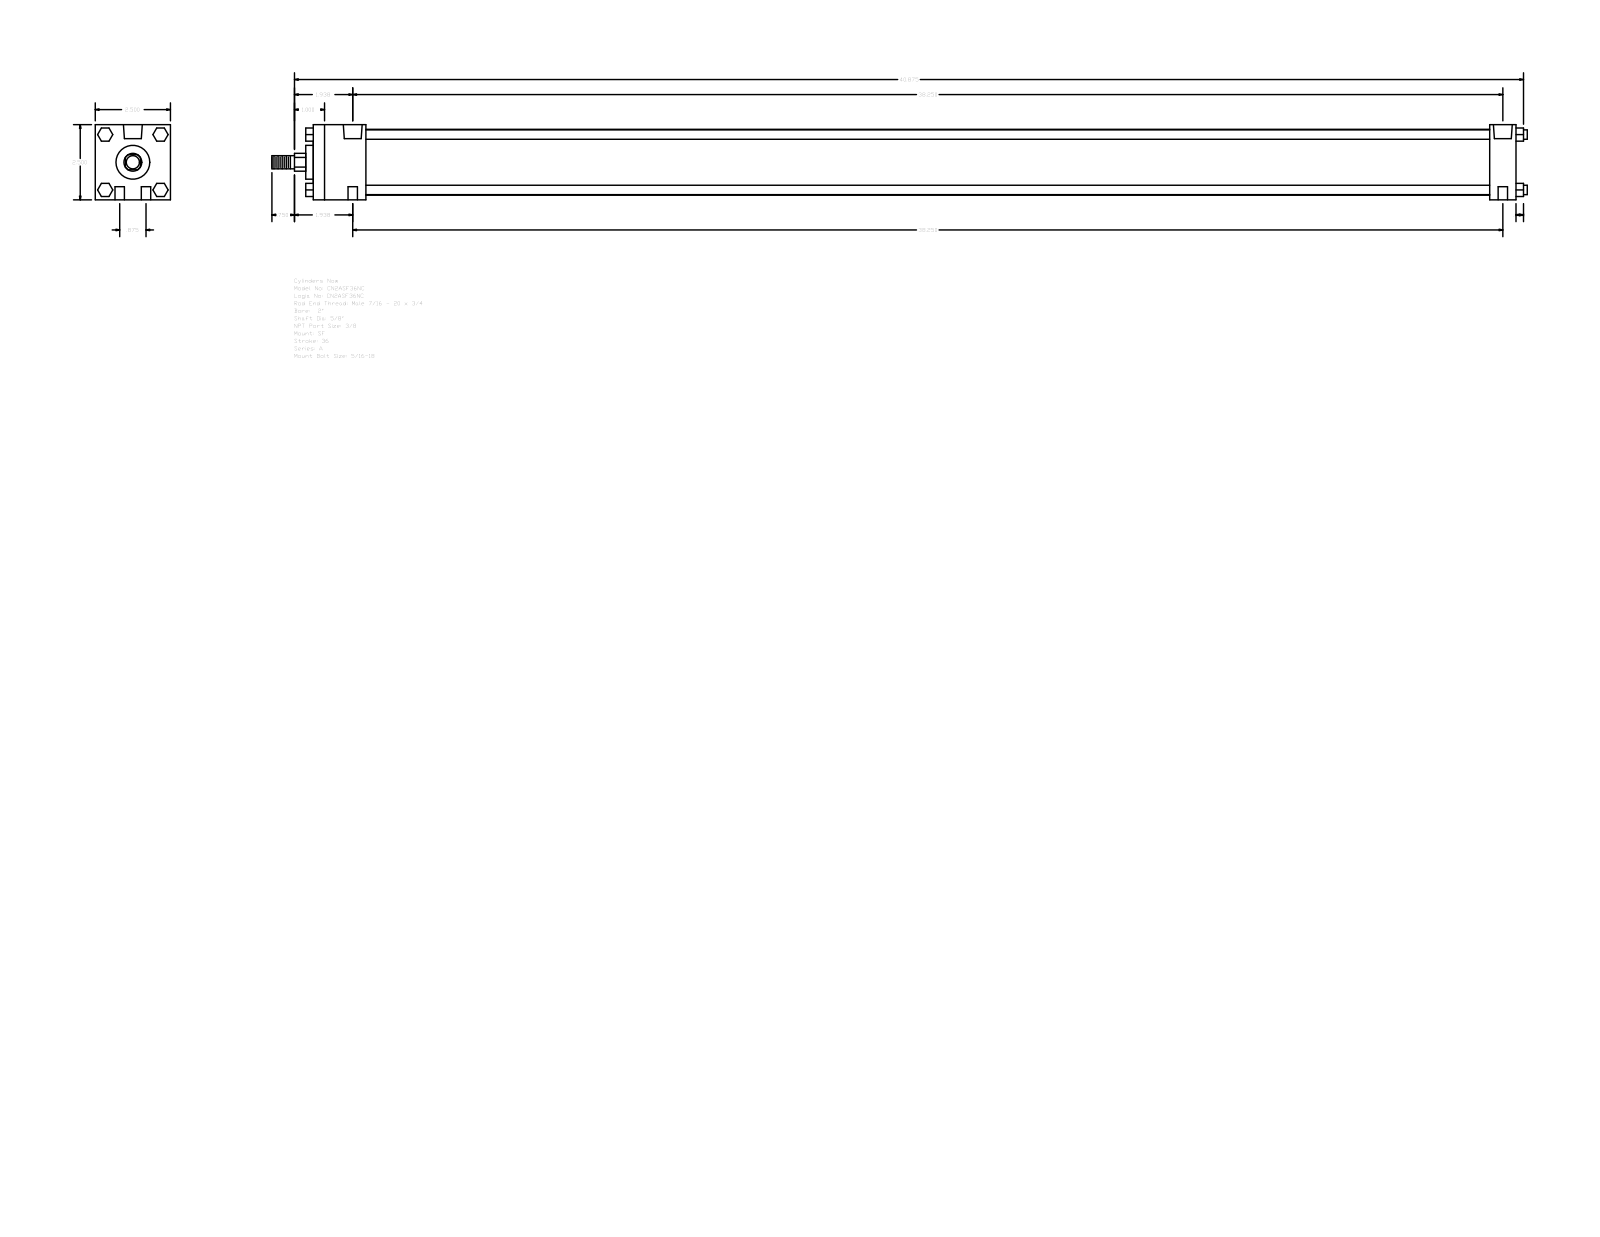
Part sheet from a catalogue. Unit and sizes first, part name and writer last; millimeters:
Units: millimetres
Overall size (bounding box): 1060.45 × 63.5 × 63.5
Round holes (diameter × count): ⌀7.94 ×4, ⌀5.56 ×2, ⌀15.93 ×2
Round bosses / shafts (diameter × count): ⌀7.94 ×4, ⌀55.63 ×1, ⌀28.57 ×1, ⌀15.88 ×1, ⌀11.11 ×1
Partial cylindrical surfaces — rounded edges, fillets, slot ends (radius × count): R7.54 ×1
Main face-to-face distances: 63.5, 1016, 993.77, 22.23, 44.45, 949.32, 971.55, 50.8, 6.35, 1000.12
Hole centre spacings: 11.11, 971.61, 971.55, 22.22, 971.8, 963.6
Bodies: 0 solids, 124 faces (94 planar, 30 cylindrical, 0 other)
Part name (STEP PRODUCT): A_SF__0200_0.625
STEP written by: GSSL Pune (CONFIG_CONTROL_DESIGN)
